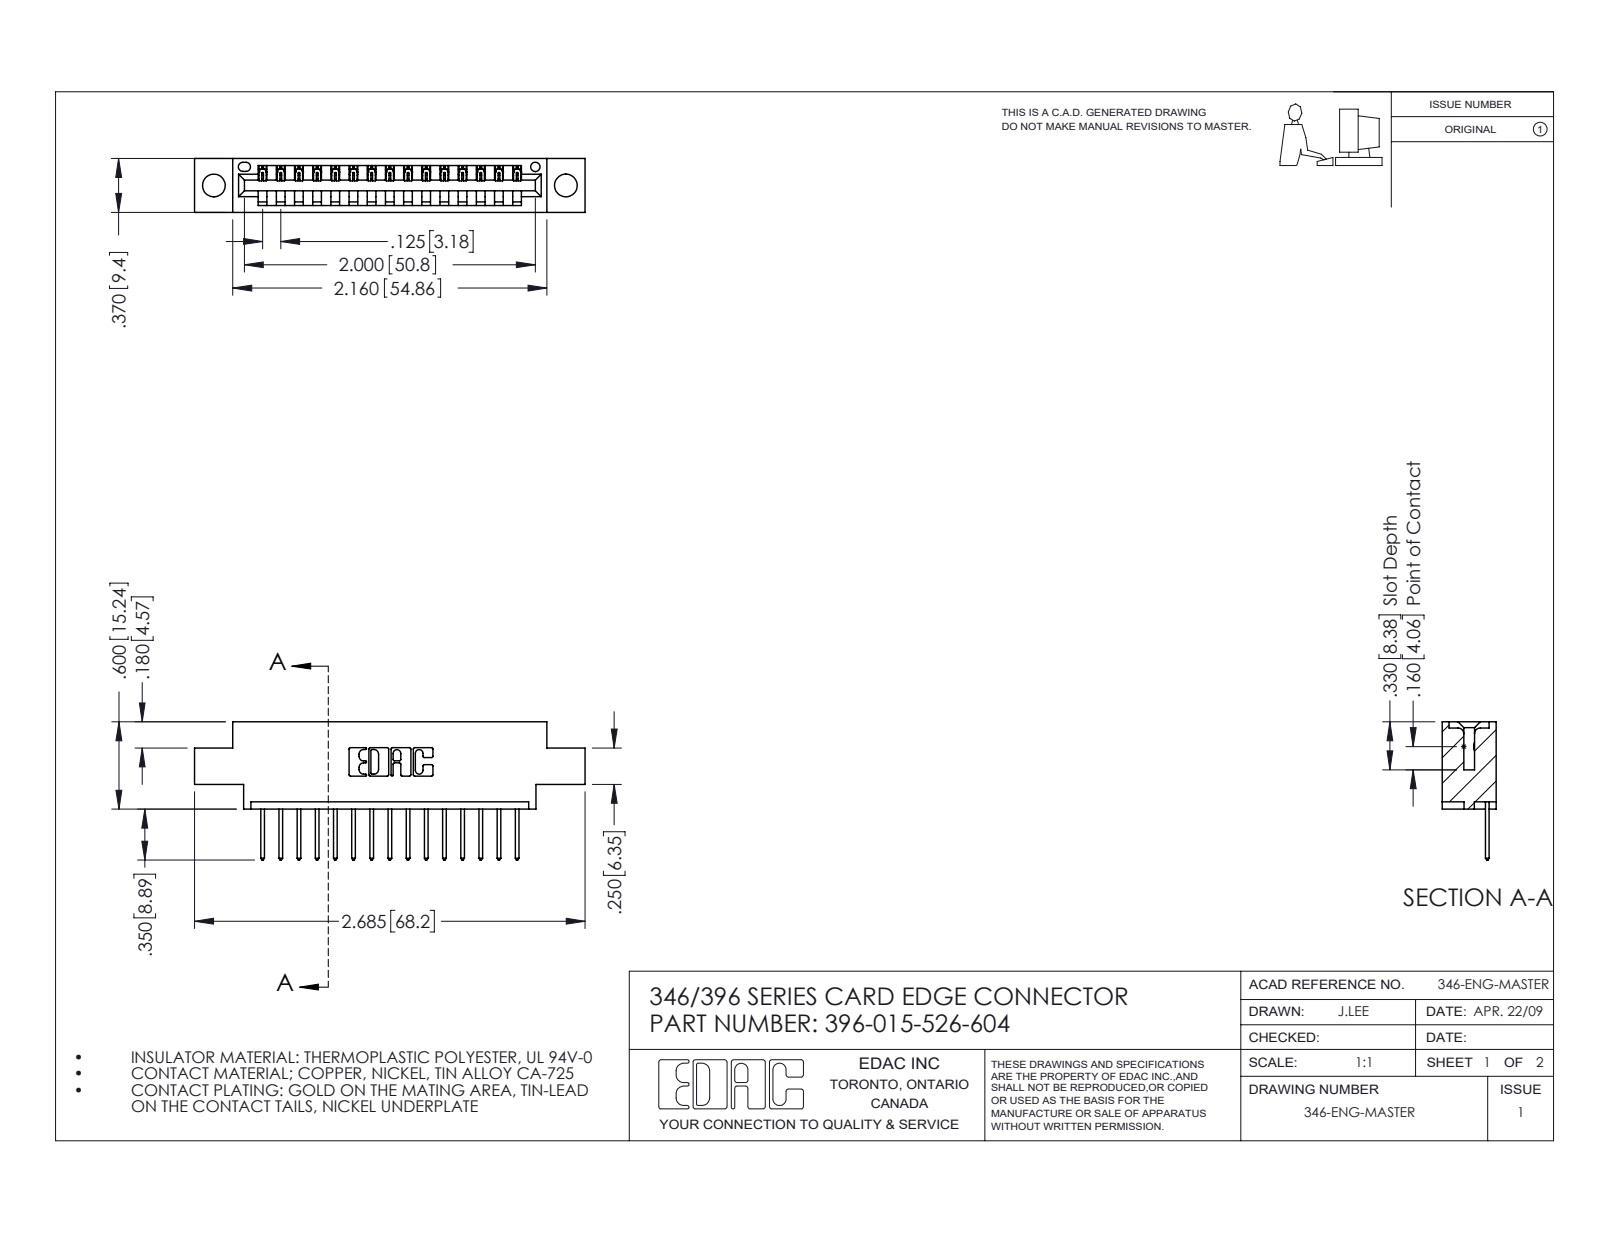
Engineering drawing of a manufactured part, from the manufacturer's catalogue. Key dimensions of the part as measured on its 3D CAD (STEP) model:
Part name (STEP PRODUCT): 396-015-526-604; 346 Part_0.170 Offset - 0.156 Dia-TH; 345-292-001_345-293-126
STEP written by: SolidWorks 2016 (CONFIG_CONTROL_DESIGN)
Units: inches
Bodies: 16 solids, 996 faces (680 planar, 316 cylindrical, 0 other)
Overall size (bounding box): 2.685 × 0.95 × 0.37
Volume: 0.371 in³ · Surface area: 11.27 in²
Round holes (diameter × count): ⌀0.156 ×2, ⌀0.064 ×1
Partial cylindrical surfaces — rounded edges, fillets, slot ends (radius × count): R0.006 ×30, R0.01 ×30, R0.01 ×22, R0.007 ×6, R0.031 ×6, R0.026 ×3, R0.031 ×2, R0.04 ×2
Main face-to-face distances: 0.048, 0.322, 0.37, 0.25, 0.072, 0.298, 0.025, 0.148, 0.222, 0.1
Hole centre spacings: 0.246, 2.213, 2.42
